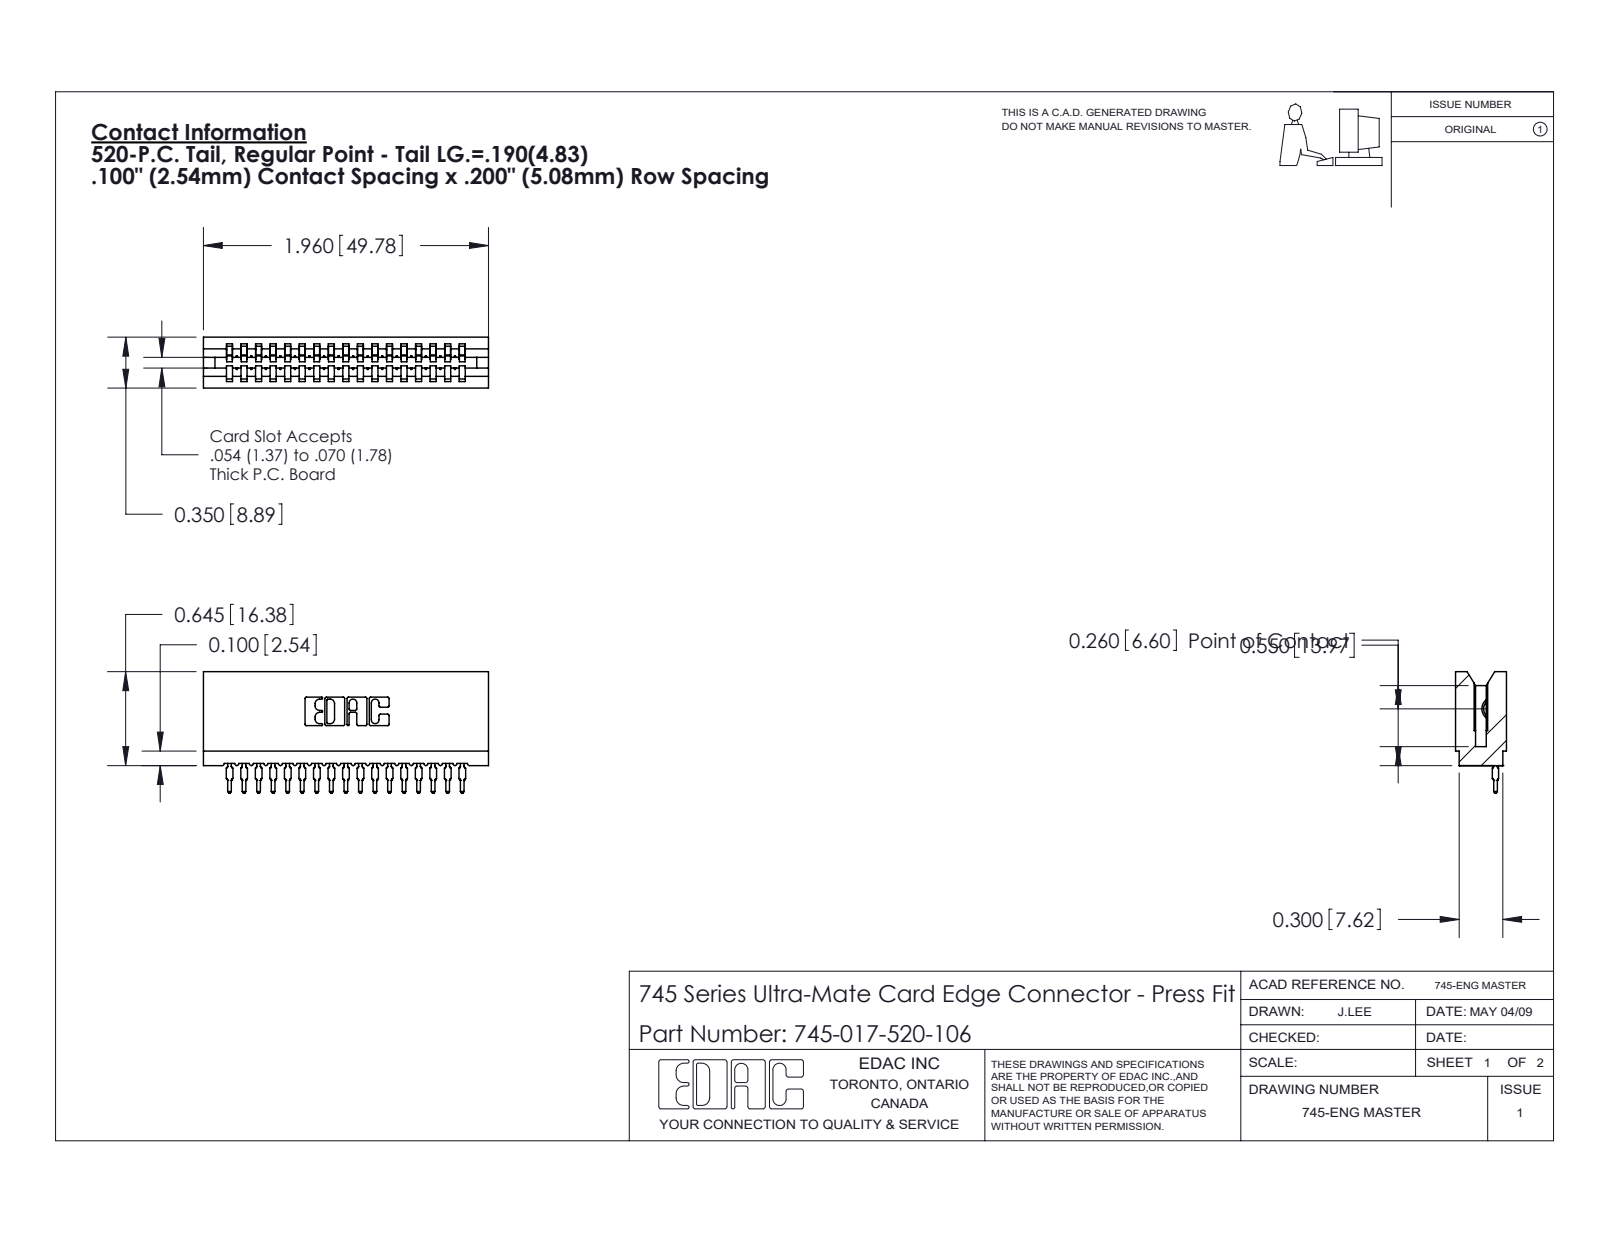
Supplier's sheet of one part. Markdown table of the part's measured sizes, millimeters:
| quantity | value |
| --- | --- |
| part name | 745-292-001_520; 745-017-520-106; 745 Part_Insulator Option - 06 |
| STEP written by | SolidWorks 2020 (CONFIG_CONTROL_DESIGN) |
| units | millimeters |
| bodies | 18 solids, 2000 faces (1195 planar, 363 cylindrical, 442 other) |
| overall size | 49.8 × 21.2 × 8.9 |
| volume | 4 420 mm³ |
| surface area | 7 690 mm² |
| partial cylindrical surfaces (radius × count) | 0.4 × 34, 0.5 × 34, 0.3 × 22, 0.2 × 6, 0.8 × 6, 0.1 × 4, 0.3 × 4, 0.7 × 3 |
| main face-to-face distances | 2.5, 5.1, 7.6, 10.2, 12.7, 8.9, 15.2, 17.8, 3.5, 5.4 |
